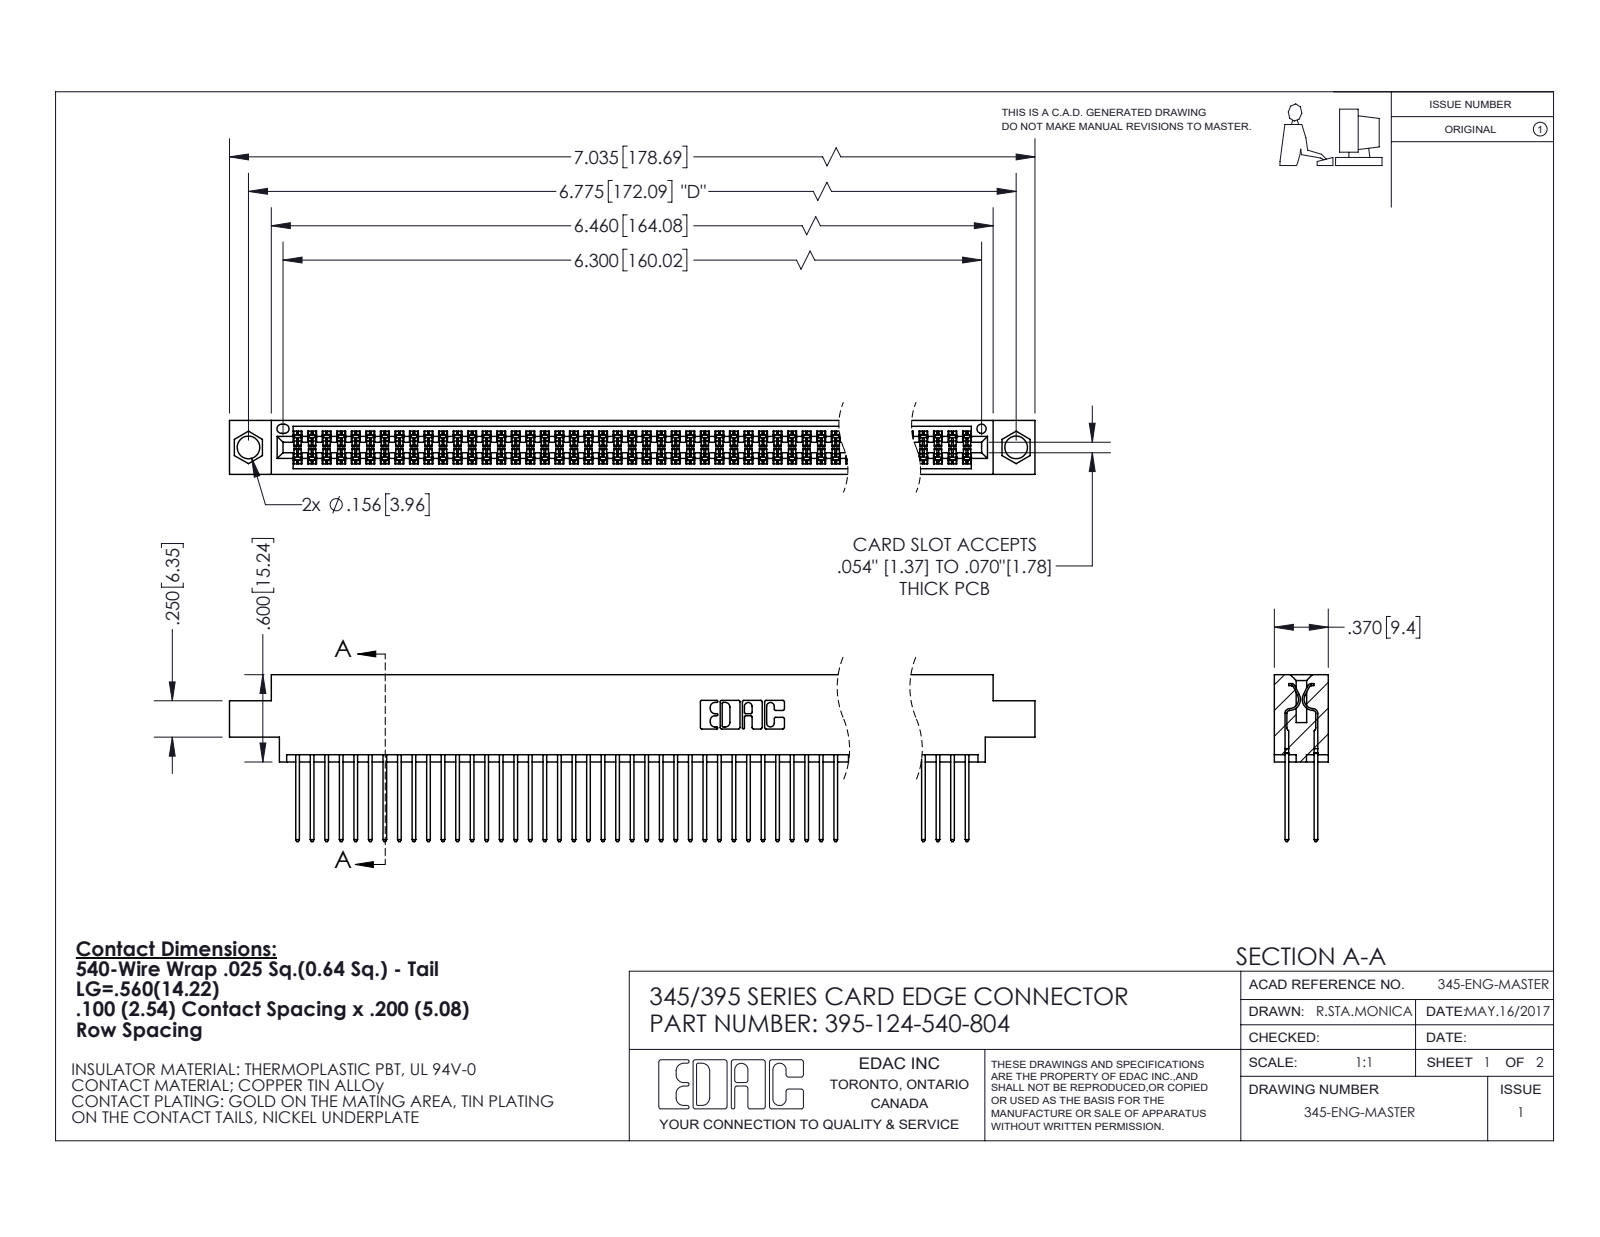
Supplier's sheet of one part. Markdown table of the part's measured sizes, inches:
| quantity | value |
| --- | --- |
| part name | 345-292-001_345-293-140; 395-124-540-804; 345 Part_0.170 Offset - 0.156 Dia-TI |
| STEP written by | SolidWorks 2020 (CONFIG_CONTROL_DESIGN) |
| units | inches |
| bodies | 125 solids, 6344 faces (4190 planar, 2154 cylindrical, 0 other) |
| overall size | 7.035 × 1.147 × 0.37 |
| volume | 1.086 in³ |
| surface area | 44.74 in² |
| round holes (diameter × count) | 0.156 × 2, 0.064 × 1 |
| partial cylindrical surfaces (radius × count) | 0.006 × 186, 0.01 × 124, 0.01 × 22, 0.007 × 6, 0.031 × 6, 0.026 × 3, 0.014 × 2, 0.019 × 2 |
| main face-to-face distances | 0.298, 0.072, 0.2, 0.098, 0.272, 0.025, 0.37, 0.225, 0.175, 0.149 |
| hole center spacings | 0.27, 6.539, 6.775 |
